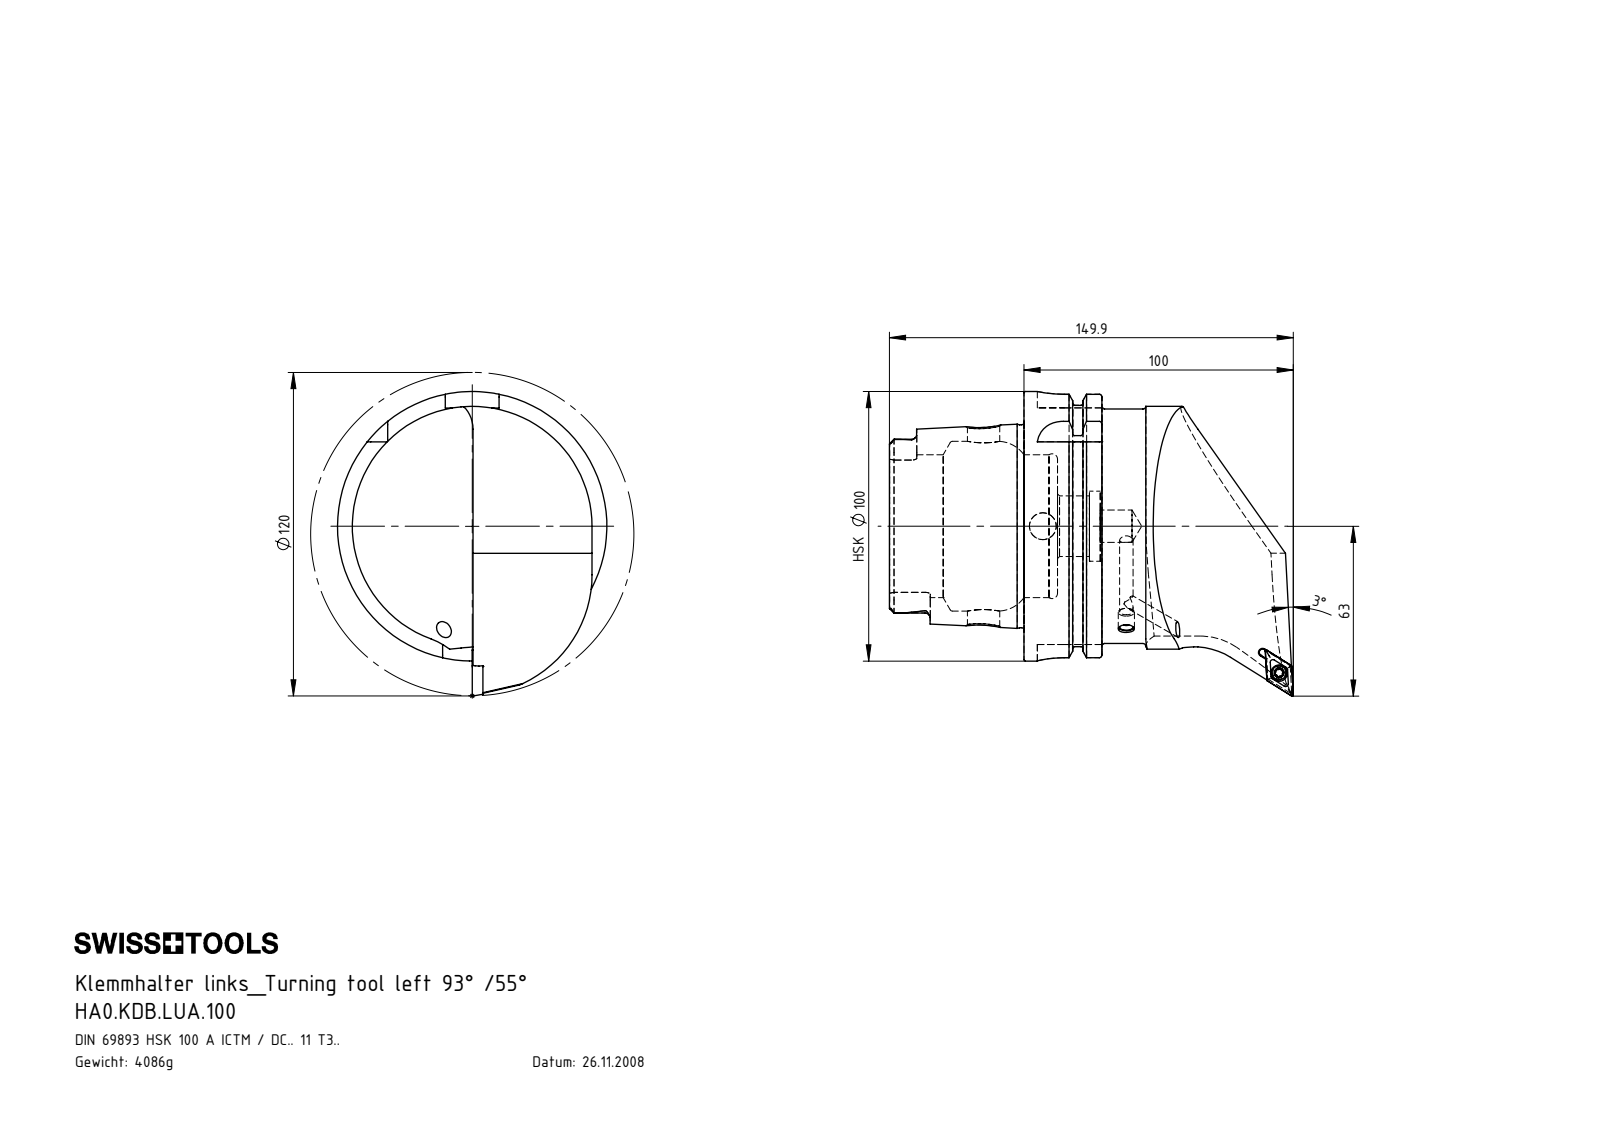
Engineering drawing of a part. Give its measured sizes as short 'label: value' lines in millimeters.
name: HA0-KDB.LUA.100_B_Fertigbearbeitung; HA0-KDB.LUA.100; KVT_MB_600_060; WCB-ER2.001.009_A (+1 more)
written by: SolidWorks 2012 (AUTOMOTIVE_DESIGN)
unit: mm
bodies: 5 solids, 310 faces (76 planar, 91 cylindrical, 143 other)
size: 149.9 × 113.01 × 100
volume: 520 305 mm³; area: 67 400 mm²
holes: 3× ⌀5, 2× ⌀12, 1× ⌀3.3, 1× ⌀4.4, 1× ⌀6, 1× ⌀6.1, 1× ⌀10, 1× ⌀22.5, 1× ⌀26, 1× ⌀53, 1× ⌀63
bosses: 1× ⌀100, 1× ⌀91.95, 1× ⌀87, 1× ⌀75.26, 1× ⌀6, 1× ⌀5.25, 1× ⌀4
rounds: 6× R0.34, 6× R0.59, 6× R1.9, 4× R10, 2× R4.83, 2× R4.88, 2× R26, 2× R44.5
face distances: 12.45, 28.95, 16.5, 49.9, 62.35, 78.85, 44.2, 87.8, 78.2, 28.3
hole spacings: 103.21, 103.32
